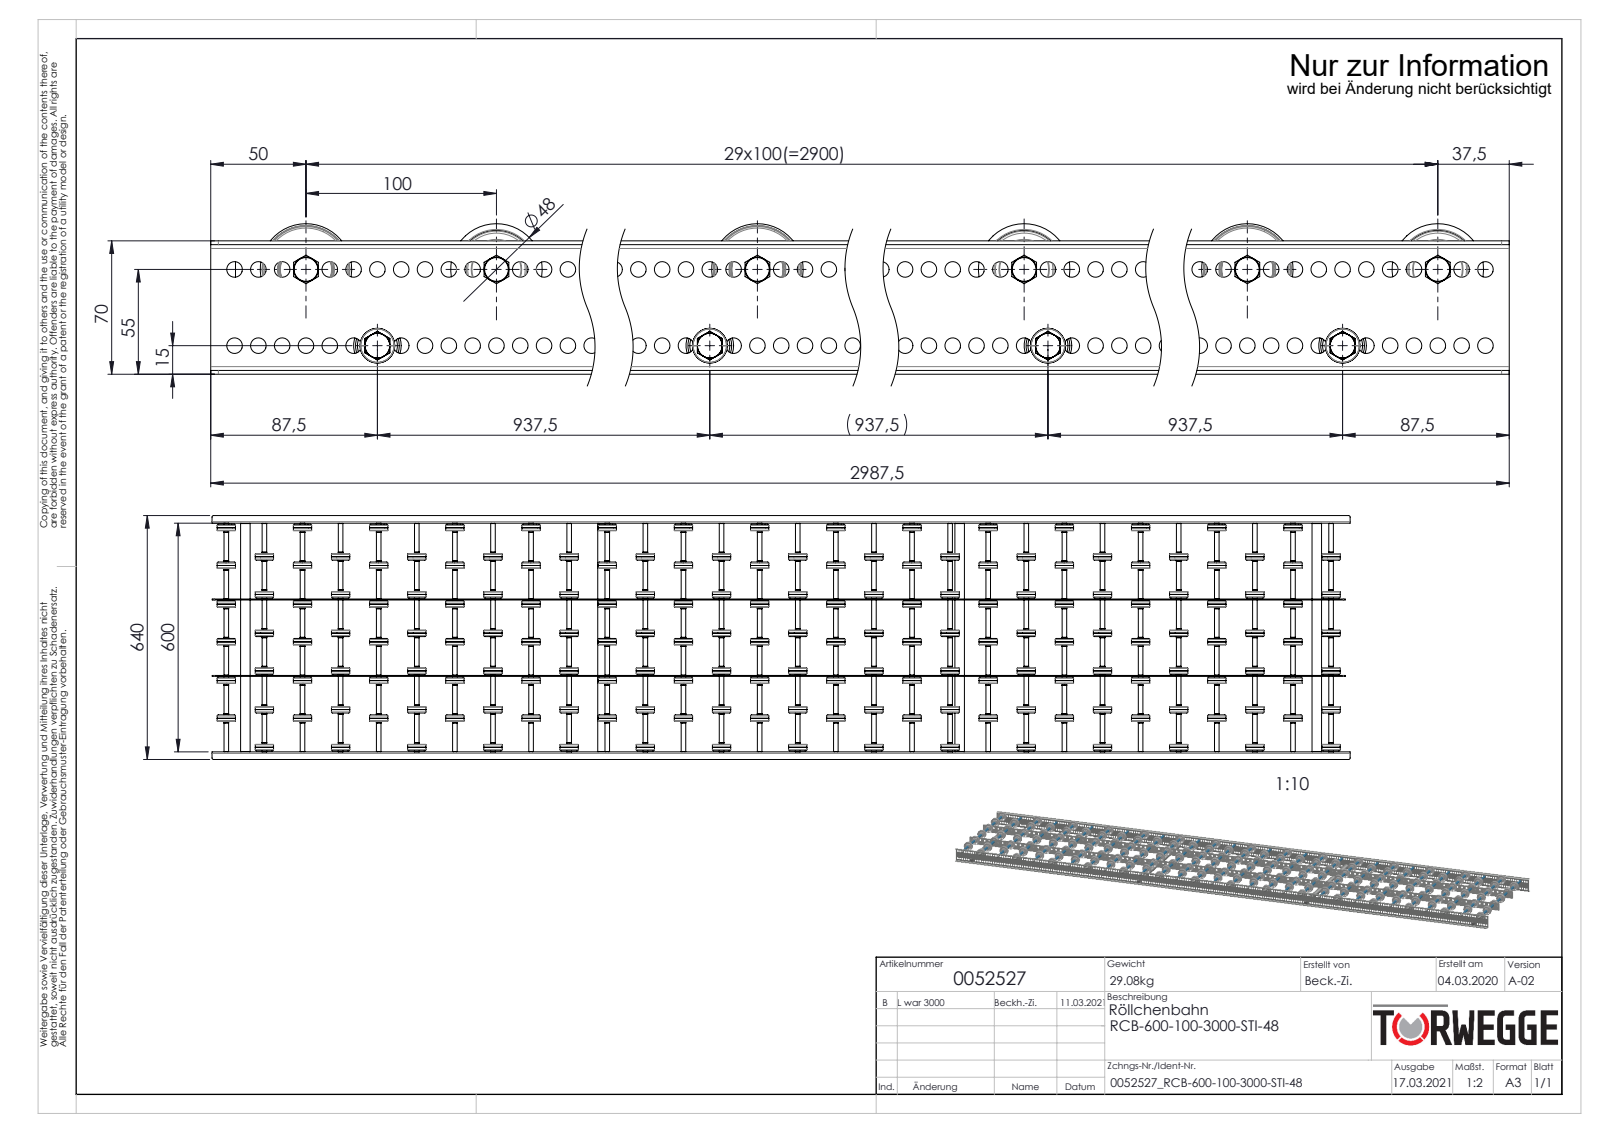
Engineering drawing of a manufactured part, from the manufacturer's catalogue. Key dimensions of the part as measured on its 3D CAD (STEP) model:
Part name (STEP PRODUCT): 0046278_KB-ROHR-12X1,75mm_KFG_L75; K0011528_2200-48-8; Profil_LRB-20x70x20x2_KFG_S109080_U-PROFIL-20-70-20-2-LRB-L=2987,5; Hutmutter_DIN_1587_M8 (+6 more)
STEP written by: SolidWorks 2020 (AUTOMOTIVE_DESIGN)
Units: millimetres
Bodies: 654 solids, 20308 faces (3996 planar, 8184 cylindrical, 8128 other)
Overall size (bounding box): 2987.5 × 640 × 79
Volume: 7 436 000 mm³ · Surface area: 5 763 000 mm²
Round holes (diameter × count): ⌀8.2 ×476, ⌀8.5 ×119, ⌀6.65 ×30, ⌀8 ×30, ⌀9.65 ×30, ⌀15 ×30, ⌀41 ×30, ⌀6.8 ×4, ⌀21 ×4
Round bosses / shafts (diameter × count): ⌀48 ×30, ⌀13 ×30, ⌀12.5 ×30, ⌀12.4 ×30, ⌀12 ×30, ⌀11.5 ×30, ⌀25 ×4, ⌀8 ×4
Partial cylindrical surfaces — rounded edges, fillets, slot ends (radius × count): R4 ×8, R2 ×4, R5 ×4
Main face-to-face distances: 200.5, 2, 401, 602, 76, 99, 2.5, 198, 111, 187
Hole centre spacings: 12.5, 25, 37.5, 50, 62.5, 75, 87.5, 100
